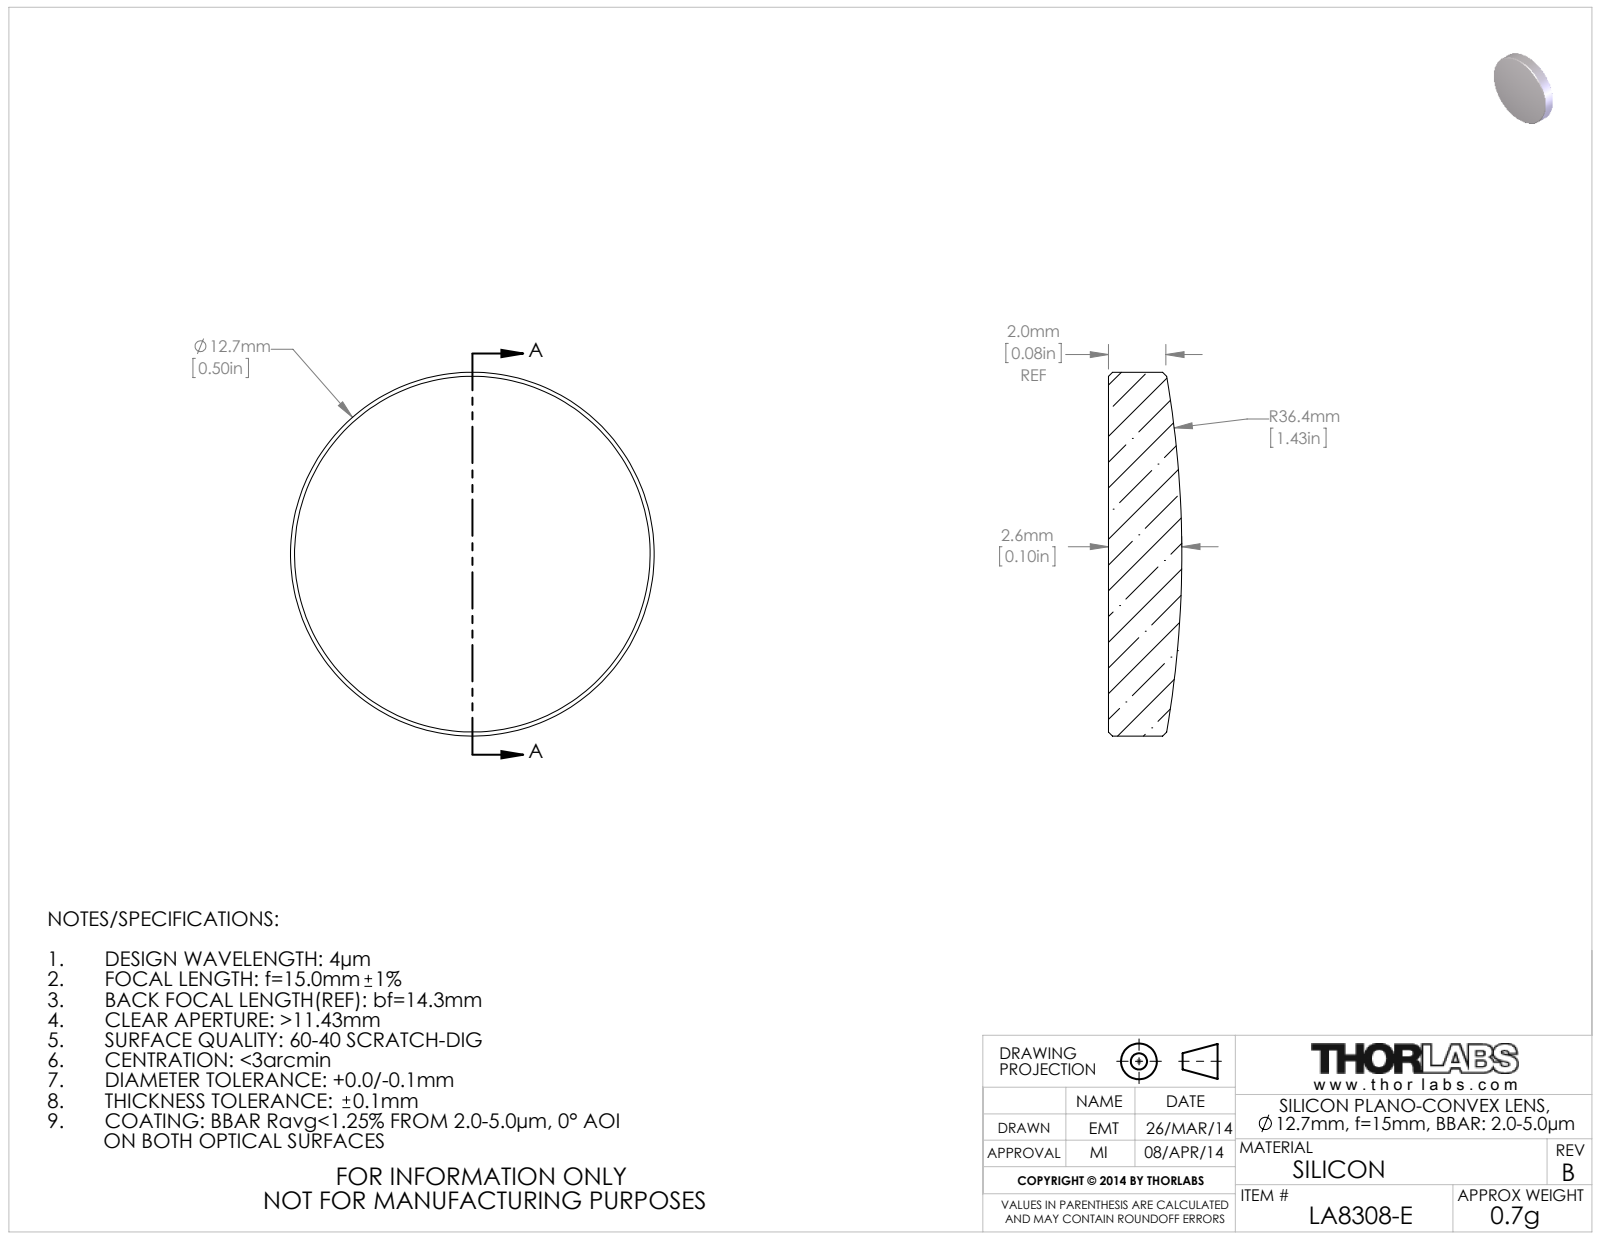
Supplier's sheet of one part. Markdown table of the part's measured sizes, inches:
| quantity | value |
| --- | --- |
| part name | 20125-E0W |
| STEP written by | SolidWorks 2014 (CONFIG_CONTROL_DESIGN) |
| units | inches |
| bodies | 1 solid, 9 faces (1 planar, 2 cylindrical, 6 other) |
| overall size | 0.5 × 0.5 × 0.101 |
| volume | 0.018 in³ |
| surface area | 0.508 in² |
| round bosses / shafts (diameter × count) | 0.5 × 1 |
